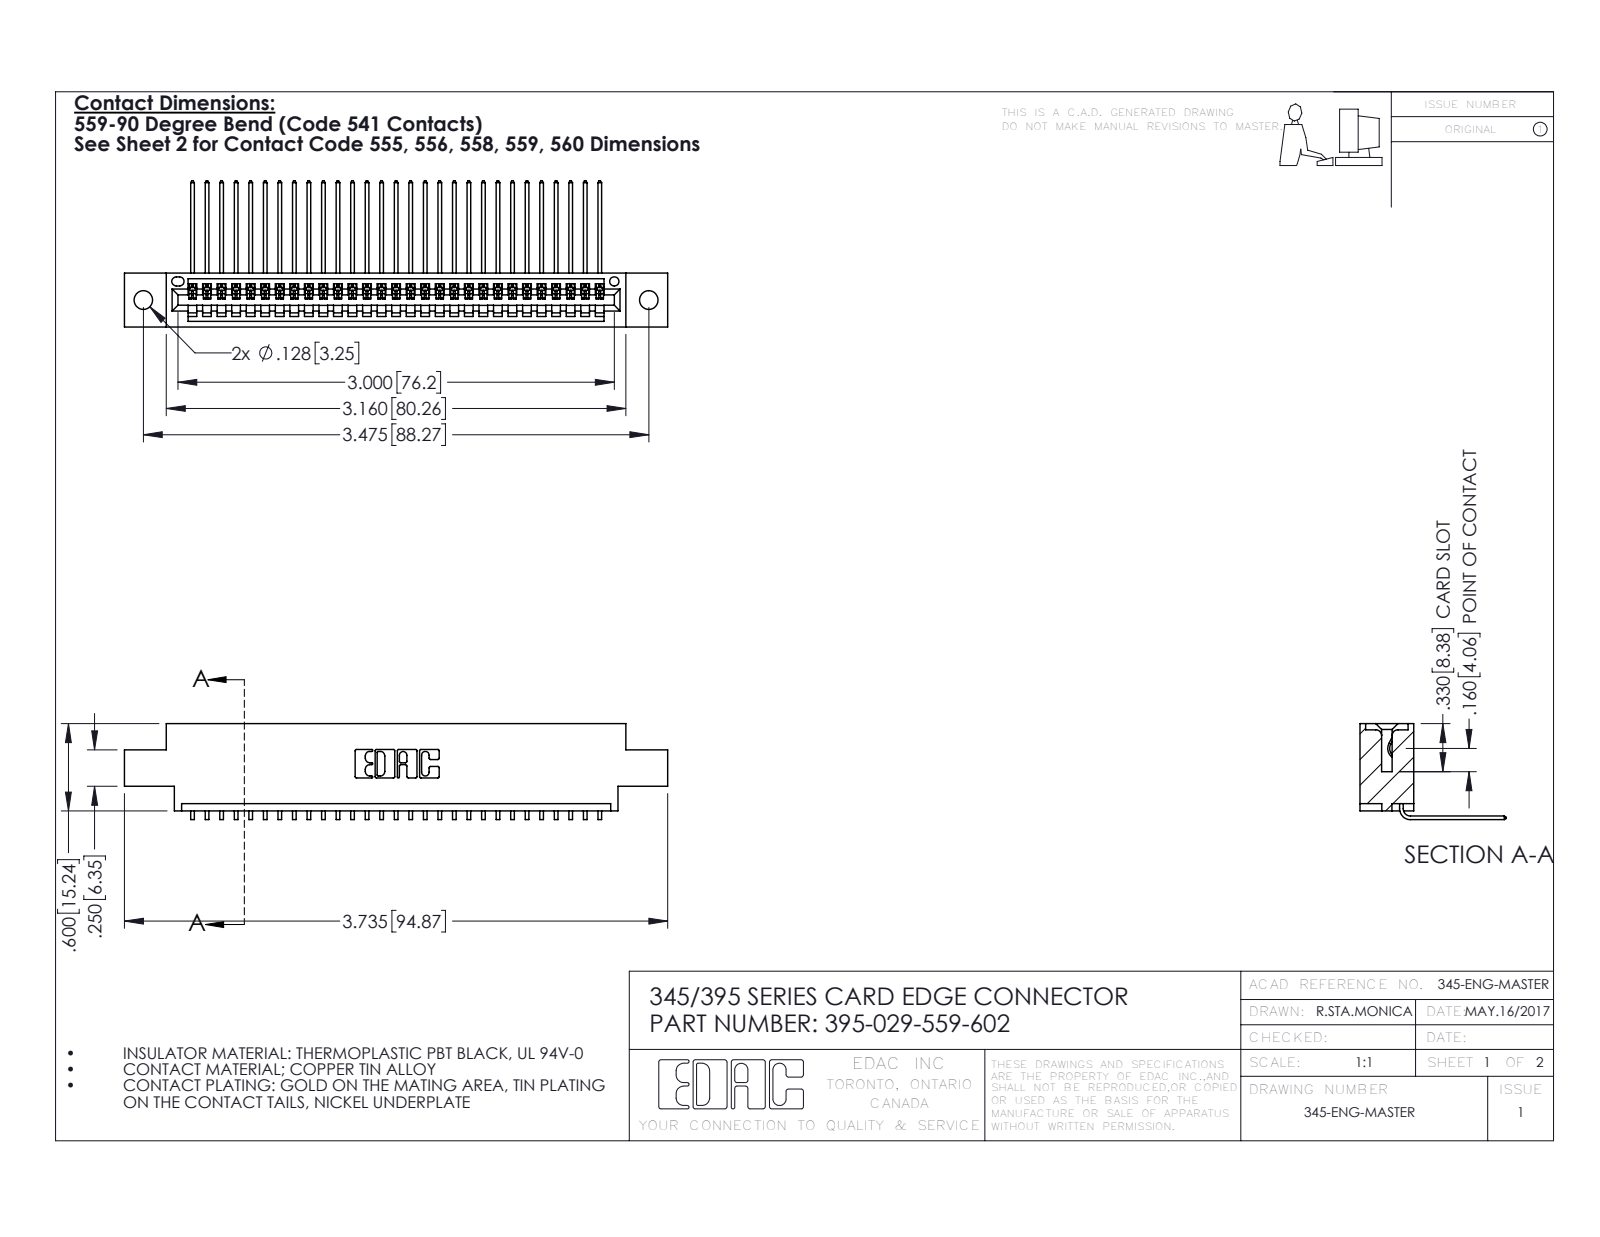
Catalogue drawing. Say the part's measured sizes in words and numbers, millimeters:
The part is named "395-029-559-602; 345 Part_0.170 Offset - 0.128 Dia; 345-292-001_558 559 Tail - 1". Its 3-D file was written by "SolidWorks 2016 (CONFIG_CONTROL_DESIGN)". It is 30 solids with 1870 faces: 1302 planar, 568 cylindrical and 0 other. Overall it measures 94.9 by 25.5 by 16.7 millimeters. Its volume is 8 850 cubic millimeters and its surface area 12 010 square millimeters. Round holes: 2 of diameter 3.3, 1 of diameter 1.6. Partial cylindrical surfaces (rounded edges, fillets, slot ends): 58 of radius 0.2, 22 of radius 0.3, 6 of radius 0.2, 6 of radius 0.8, 3 of radius 0.7, 2 of radius 0.8, 2 of radius 1, 1 of radius 0.4. The main face-to-face distances are 1.8, 7.6, 9.4, 5.1, 2.5, 6.9, 0.6, 5.7, 4.4, 3.8. The hole center spacings are 6.9, 82.3, 88.3.
